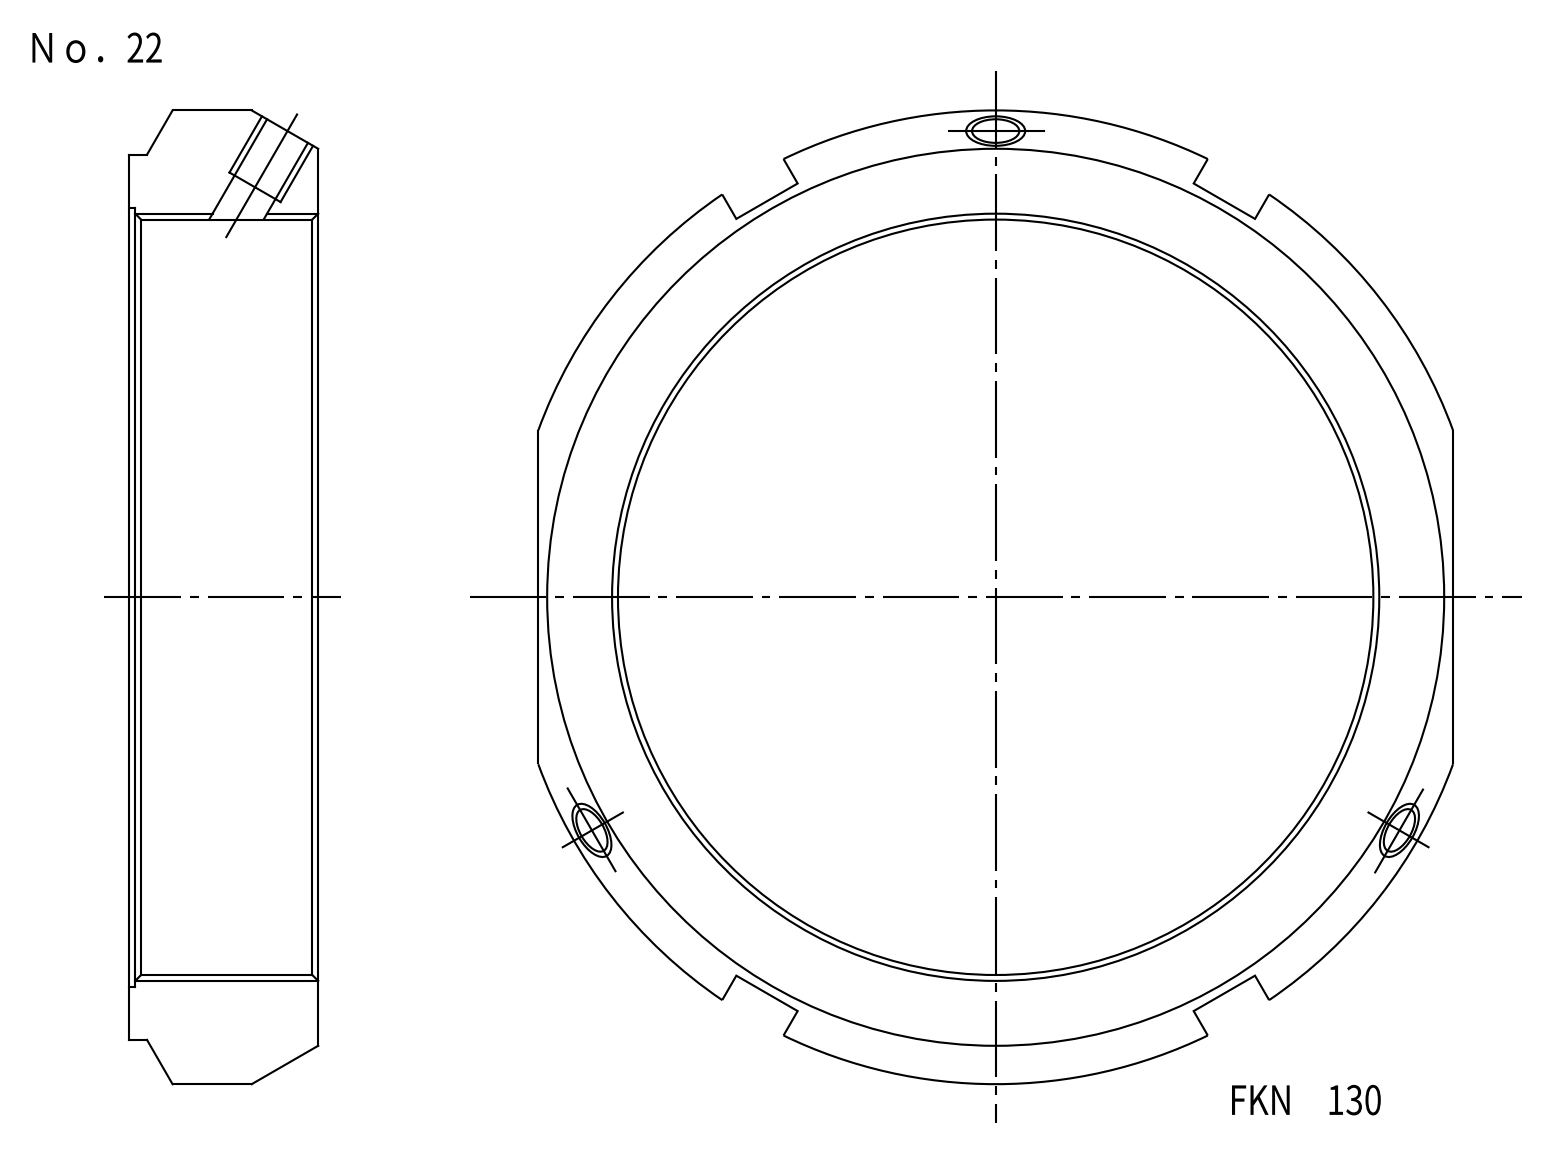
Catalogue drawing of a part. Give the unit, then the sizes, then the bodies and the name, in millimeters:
Units: millimetres
Overall size (bounding box): 165 × 155 × 32
Round holes (diameter × count): ⌀8.38 ×3, ⌀10.2 ×3, ⌀130 ×1, ⌀132 ×1
Round bosses / shafts (diameter × count): ⌀150 ×1
Partial cylindrical surfaces — rounded edges, fillets, slot ends (radius × count): R82.5 ×1
Main face-to-face distances: 32, 155, 1.5, 30.5, 12
Volume: 207 106 mm³ · Surface area: 42 545 mm²
Bodies: 1 solid, 37 faces (20 planar, 15 cylindrical, 2 other)
Part name (STEP PRODUCT): FKD FKN130
STEP written by: Autodesk Inventor LT (CONFIG_CONTROL_DESIGN)
